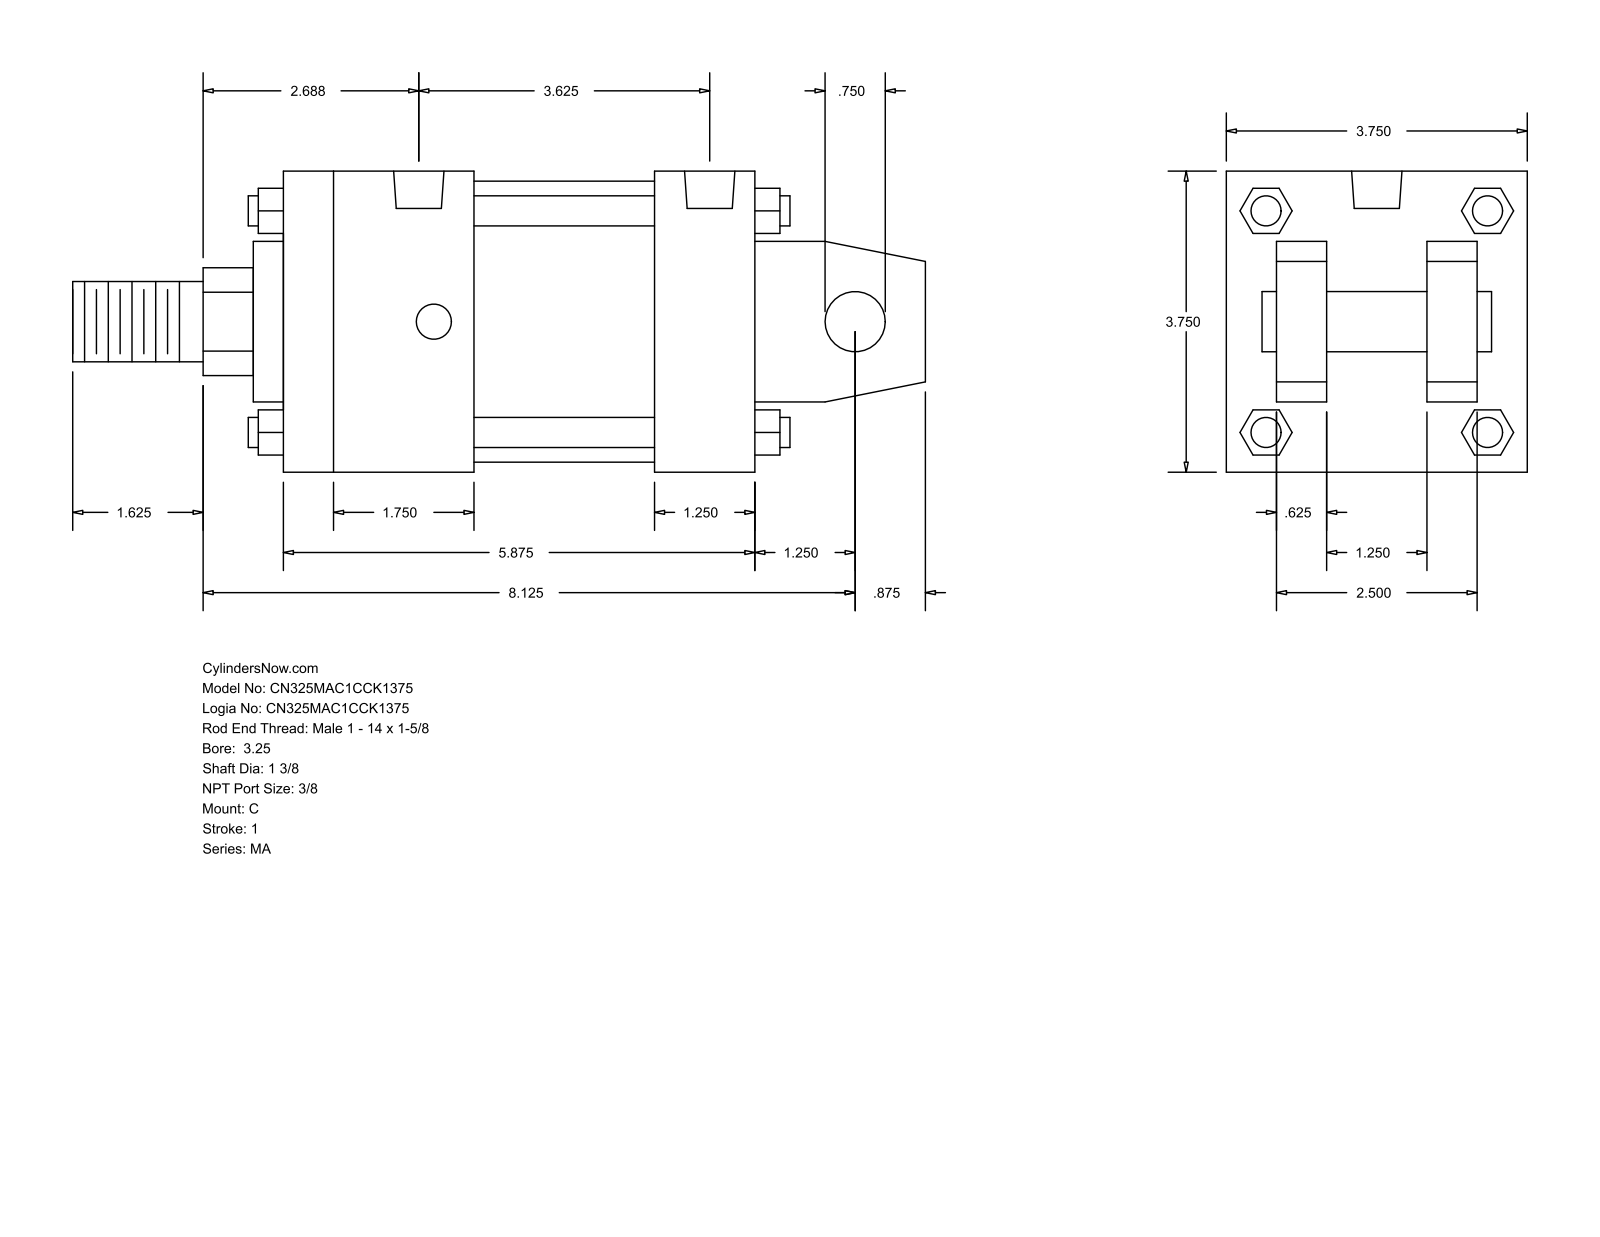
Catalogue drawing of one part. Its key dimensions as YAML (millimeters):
part_name: "MA_C__0325_1.375"
step_written_by: "GSSL Pune (CONFIG_CONTROL_DESIGN)"
units: millimeters
bodies: {solids: 0, faces: 139, planar: 108, cylindrical: 31, other: 0}
overall_size: [269.88, 95.25, 95.25]
round_holes:
  - {diameter: 11.11, count: 4}
  - {diameter: 15.93, count: 2}
round_bosses_or_shafts:
  - {diameter: 9.53, count: 4}
  - {diameter: 88.9, count: 1}
  - {diameter: 50.8, count: 1}
  - {diameter: 34.92, count: 1}
  - {diameter: 25.4, count: 1}
  - {diameter: 19.05, count: 1}
partial_cylinders:
  - {radius: 17.06, count: 1}
face_to_face_distances: [95.24, 15.87, 31.74, 63.5, 149.22, 79.37, 47.63, 117.48, 60.32, 57.16]
hole_center_spacings: [4.77, 82.54, 87.31, 92.08]
